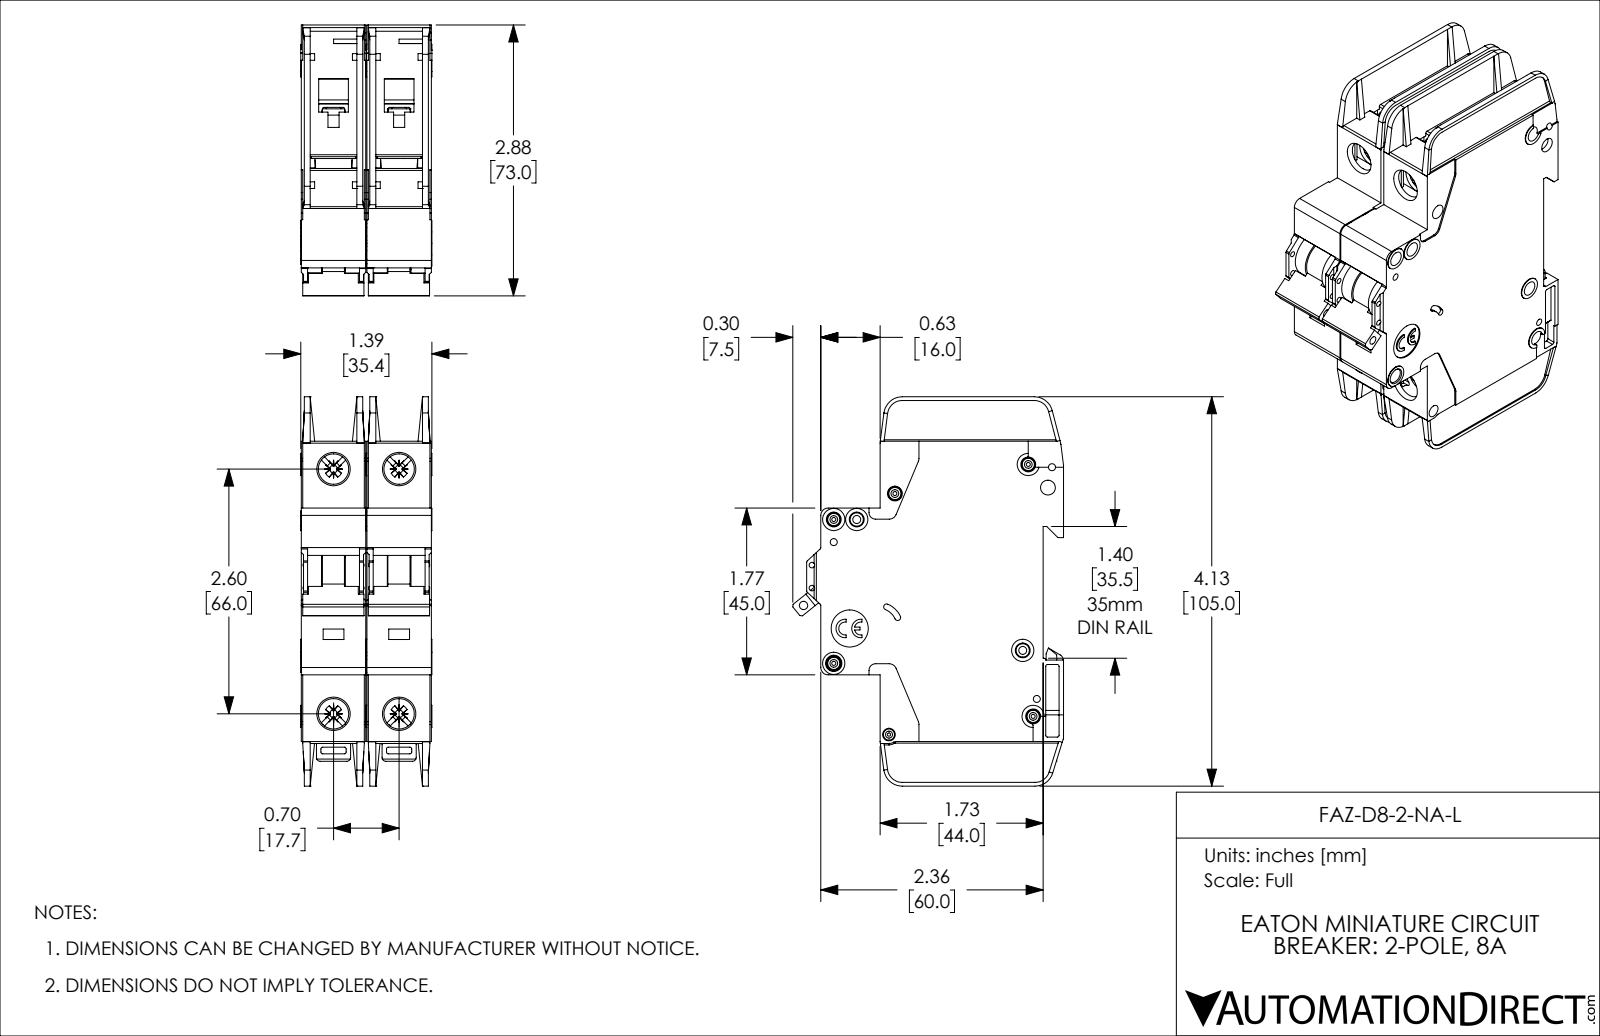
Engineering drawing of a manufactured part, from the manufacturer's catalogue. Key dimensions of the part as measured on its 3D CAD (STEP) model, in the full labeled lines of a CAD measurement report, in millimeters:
Part name (STEP PRODUCT): FAZ-D8-2-NA-L
STEP written by: SolidWorks 2019 (AUTOMOTIVE_DESIGN)
Units: millimetres
Bodies: 2 solids, 2254 faces (1342 planar, 714 cylindrical, 198 other)
Overall size (bounding box): 105 × 73.1 × 35.4
Volume: 153 500 mm³ · Surface area: 52 910 mm²
Round holes (diameter × count): ⌀4 ×8, ⌀1.1 ×5, ⌀1.9 ×4, ⌀8.2 ×4, ⌀1.5 ×2, ⌀2.2 ×2, ⌀0.9 ×1, ⌀2.3 ×1, ⌀2.5 ×1, ⌀3.4 ×1, ⌀10 ×1
Round bosses / shafts (diameter × count): ⌀3.3 ×5, ⌀6 ×4, ⌀3 ×3, ⌀2.5 ×2
Partial cylindrical surfaces — rounded edges, fillets, slot ends (radius × count): R0.5 ×57, R0.4 ×20, R1 ×14, R2 ×10, R1.1 ×8, R0.2 ×5, R5 ×5, R0.3 ×4
Main face-to-face distances: 17.7, 1.2, 17.4, 15, 2.4, 16.2, 13.8, 35.1, 18.9, 16.5
Hole centre spacings: 6.2, 13.6, 17.7, 22.1, 66, 68.3, 4.8, 5.1
